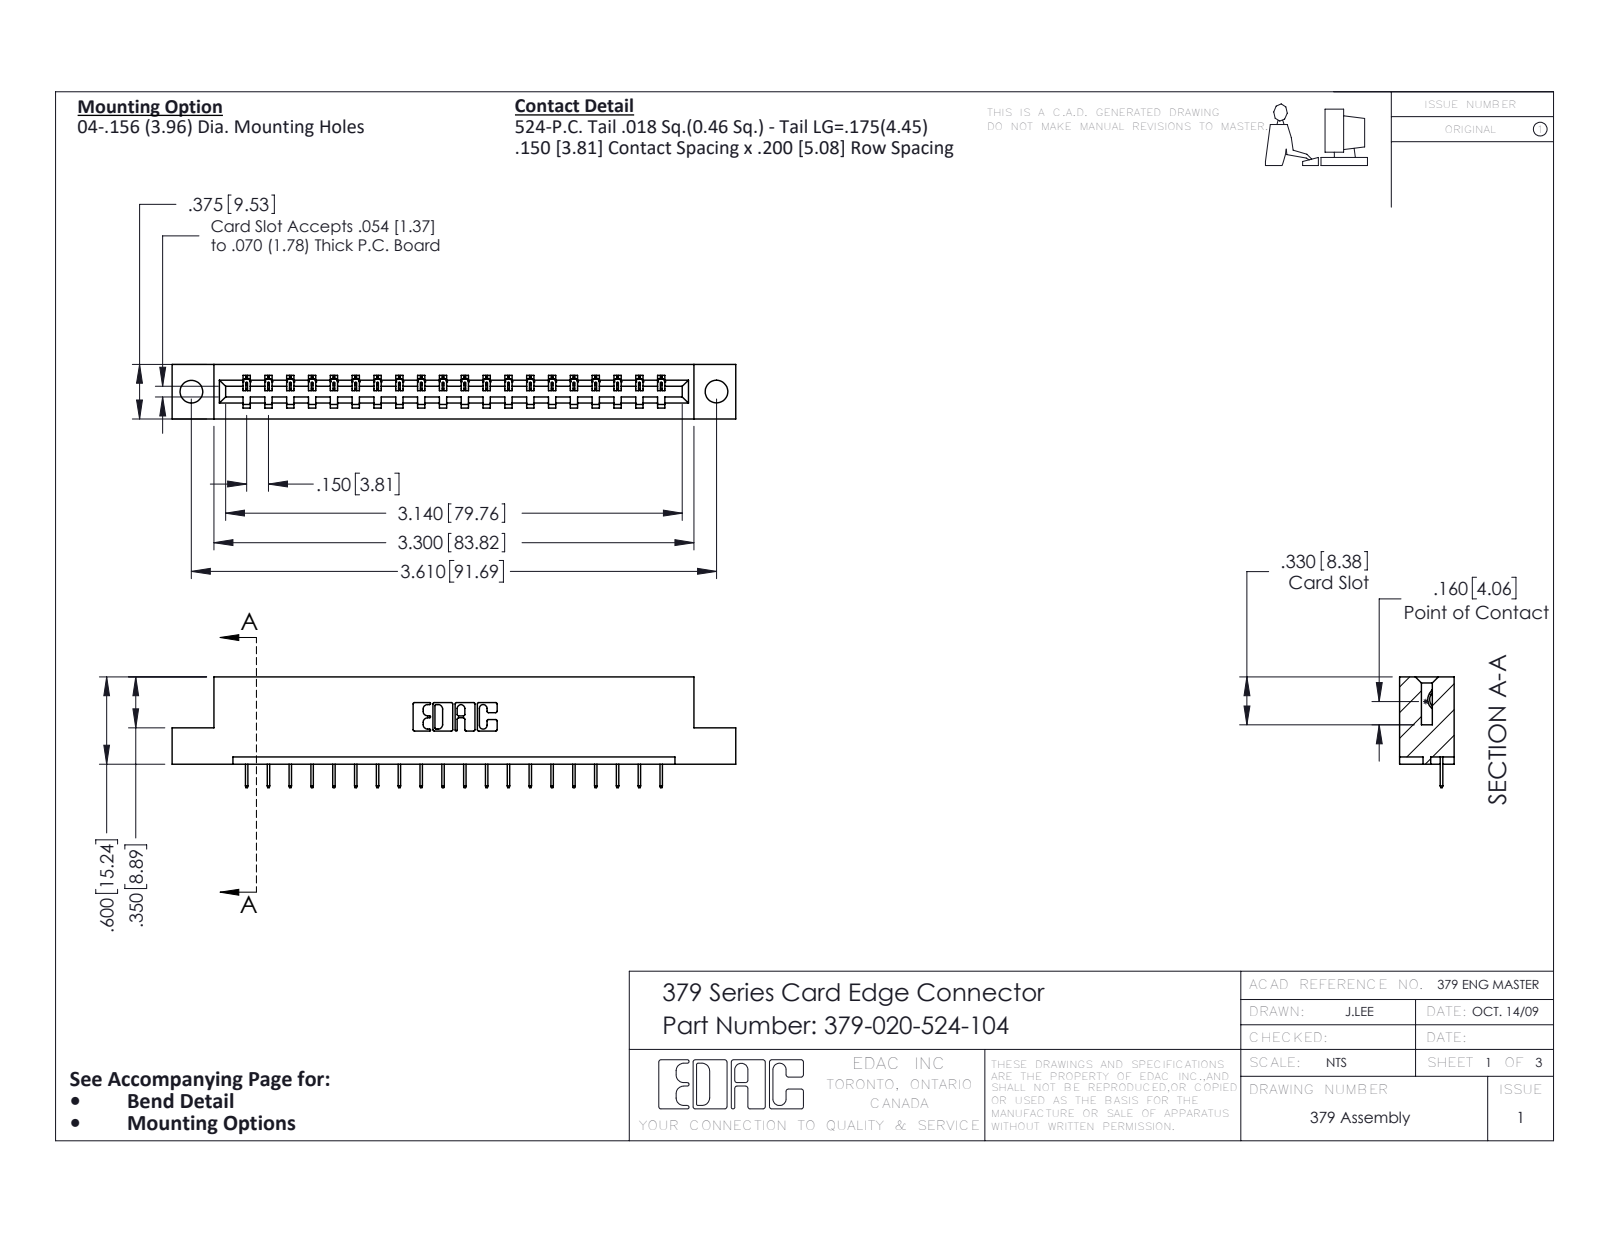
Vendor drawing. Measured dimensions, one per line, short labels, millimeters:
name: 379-020-524-104; 345-292-001_345-293-124; 379 Part_Flush - .156 Dia - TH
written by: SolidWorks 2016 (CONFIG_CONTROL_DESIGN)
unit: mm
bodies: 21 solids, 1354 faces (1030 planar, 324 cylindrical, 0 other)
size: 98.4 × 19.4 × 9.5
volume: 9 910 mm³; area: 9 548 mm²
holes: 2× ⌀4
rounds: 40× R0.2, 22× R0.3, 6× R0.2, 6× R0.8, 3× R0.7, 1× R0.4, 1× R0.6, 1× R0.6
face distances: 7.6, 9.5, 1.9, 15.2, 5.7, 3.8, 11.4, 19.1, 5.1, 14
hole spacings: 91.7
